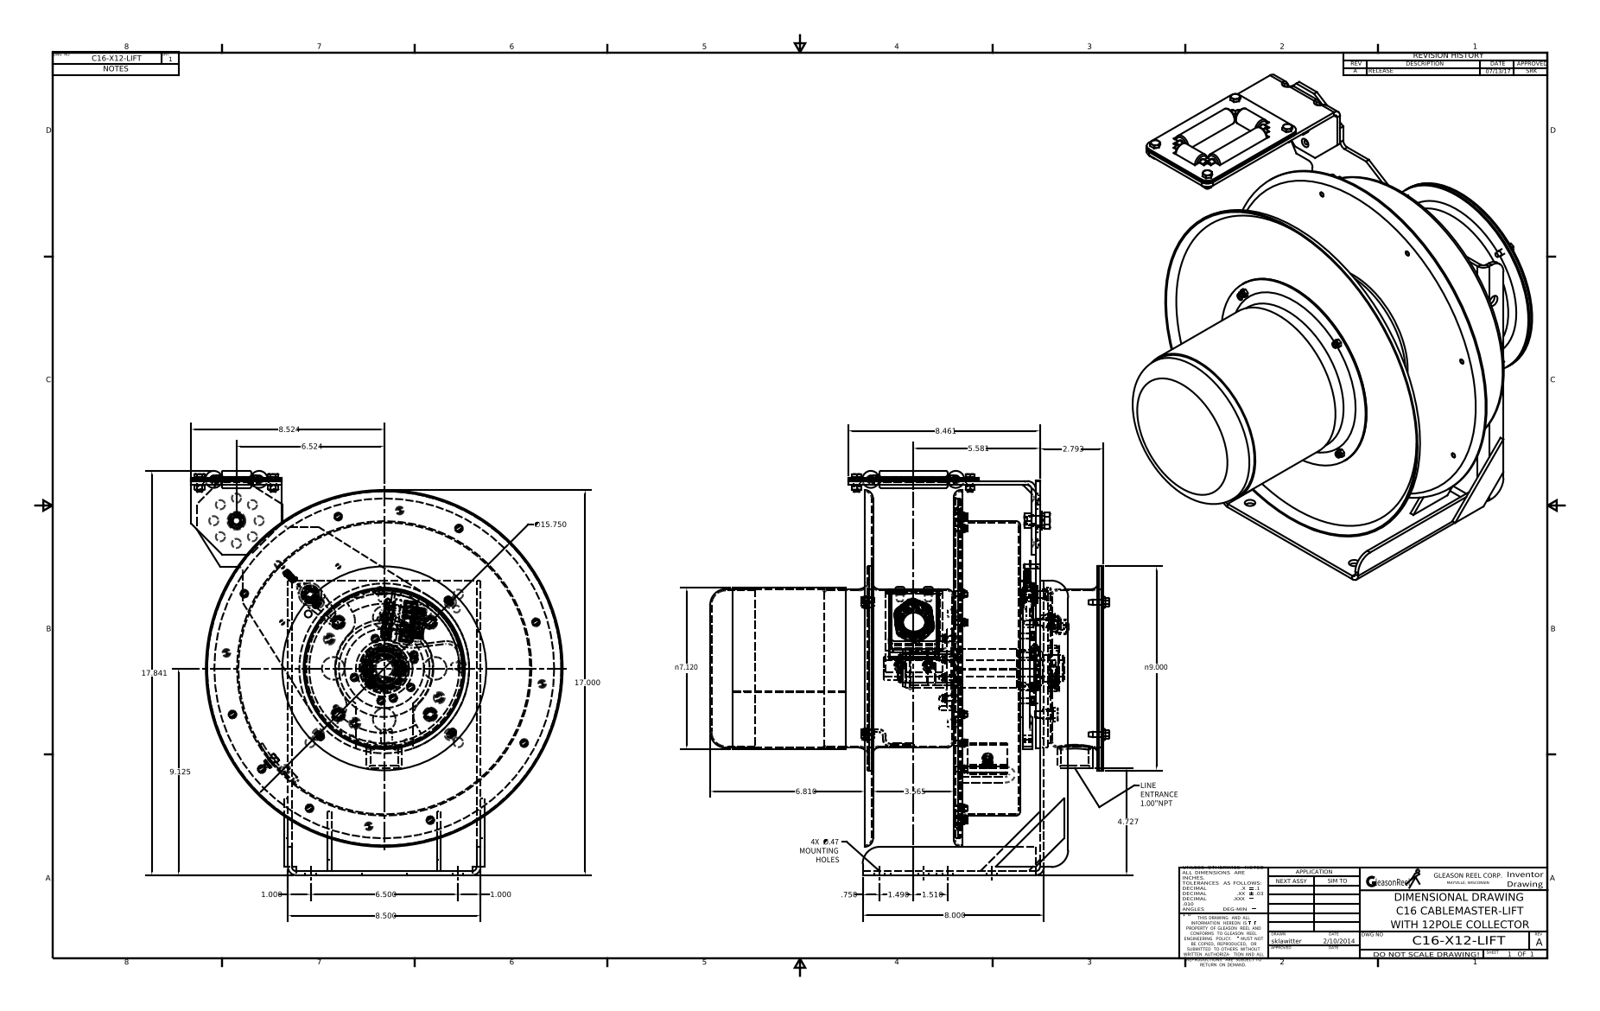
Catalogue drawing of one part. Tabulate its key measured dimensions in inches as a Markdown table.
| quantity | value |
| --- | --- |
| part name | C16-X12-LIFT (SW) |
| STEP written by | Autodesk Inventor 2016 (AUTOMOTIVE_DESIGN) |
| units | inches |
| bodies | 160 solids, 3264 faces (1283 planar, 1024 cylindrical, 957 other) |
| overall size | 17.841 × 17.605 × 16.399 |
| volume | 196.4 in³ |
| surface area | 4 205 in² |
| round holes (diameter × count) | 0.25 × 28, 0.197 × 26, 0.163 × 22, 0.406 × 13, 0.219 × 12, 0.213 × 8, 0.42 × 8, 0.47 × 8, 0.281 × 7, 0.194 × 5, 1 × 5, 0.091 × 4 |
| round bosses / shafts (diameter × count) | 0.197 × 26, 0.268 × 13, 0.236 × 10, 0.5 × 5, 0.457 × 5, 0.35 × 5, 0.315 × 5, 0.75 × 4 |
| partial cylindrical surfaces (radius × count) | 0.03 × 67, 0.009 × 64, 0.015 × 58, 0.078 × 18, 0.006 × 12, 0.06 × 12, 0.124 × 8, 0.25 × 8 |
| main face-to-face distances | 0.06, 0.179, 0.125, 6.497, 0.185, 3.809, 3.869, 0.06, 0.059, 0.244 |
| hole center spacings | 4.063, 1.749, 4.065, 5.746, 7.5, 1.754, 1.848, 1.94 |
